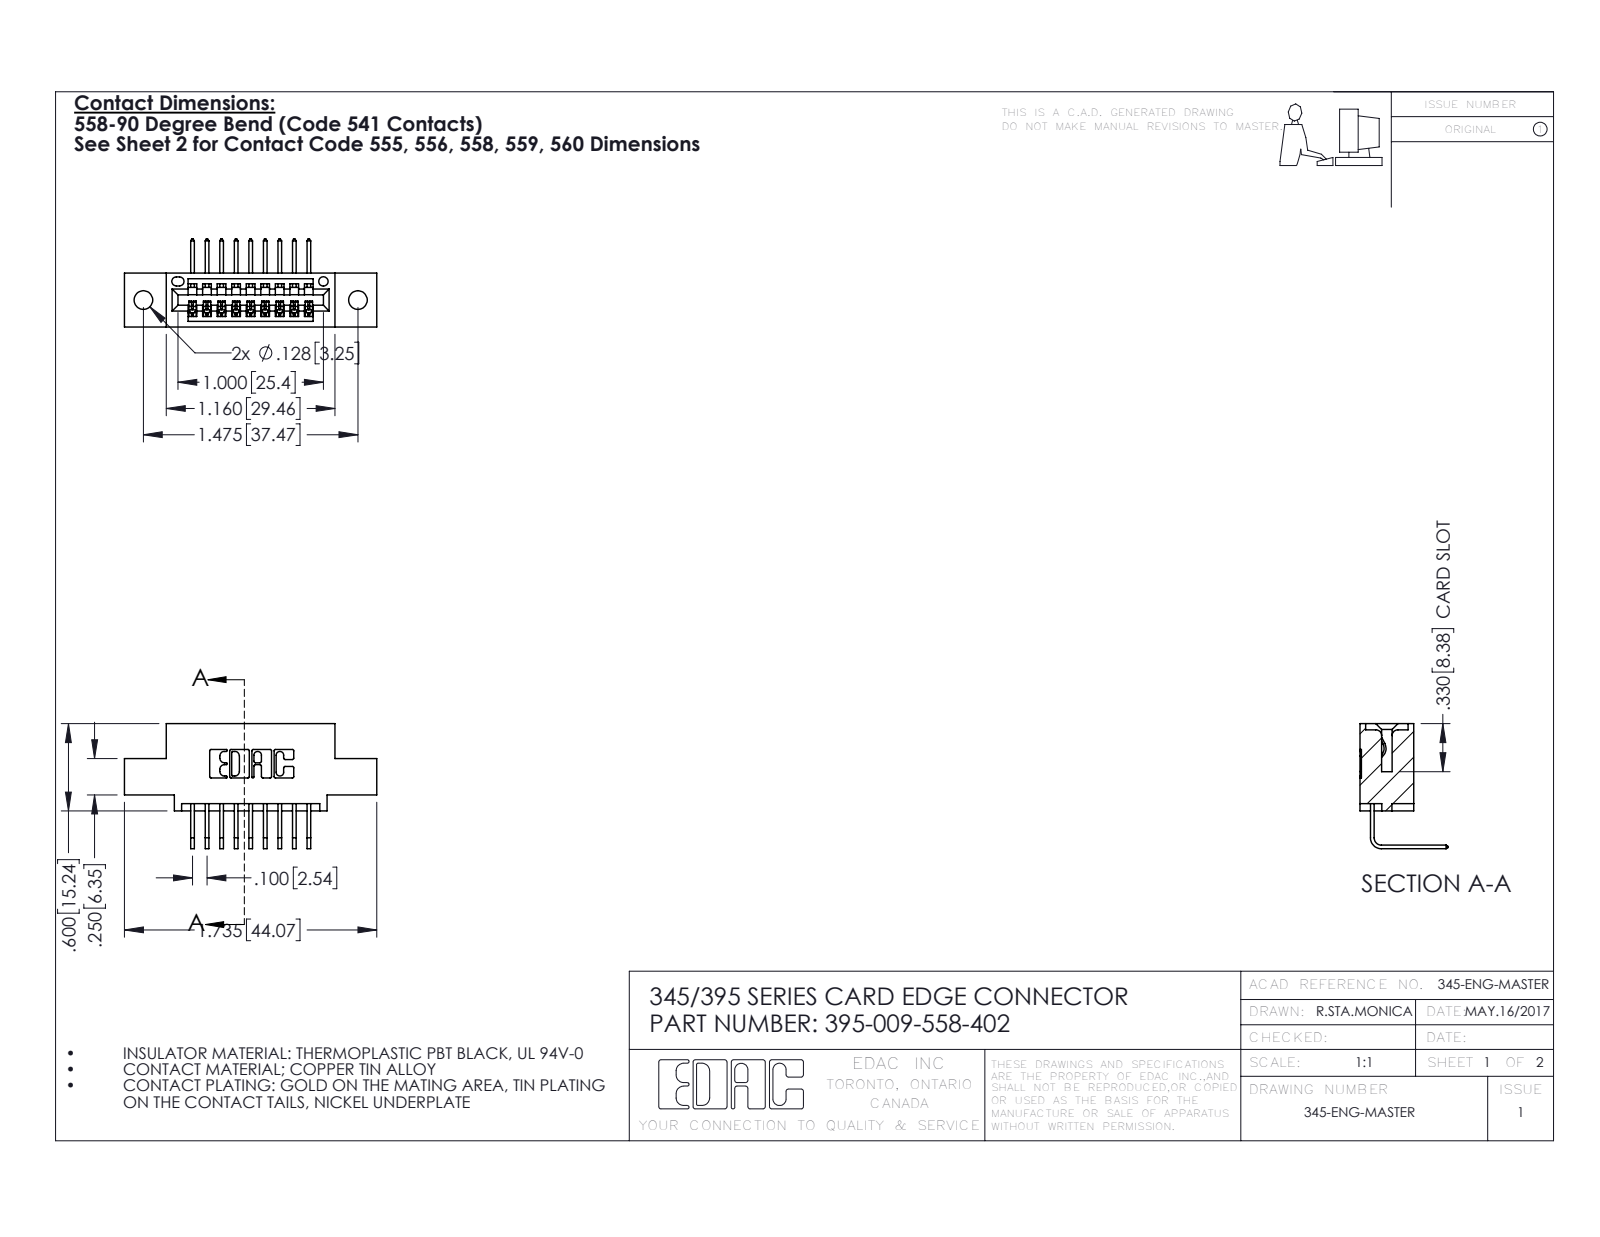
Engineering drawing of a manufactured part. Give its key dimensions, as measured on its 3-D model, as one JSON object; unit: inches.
{"part_name": "395-009-558-402; 345-292-001_558 Tail - 2; 345 Part_0.110 Offset - 0.128 Dia", "step_written_by": "SolidWorks 2016 (CONFIG_CONTROL_DESIGN)", "units": "inches", "bodies": {"solids": 10, "faces": 670, "planar": 462, "cylindrical": 208, "other": 0}, "overall_size": [1.735, 0.859, 0.605], "volume_in3": 0.234, "surface_area_in2": 7.184, "round_holes": [[0.128, 2], [0.064, 1]], "partial_cylinders_radius": [[0.01, 22], [0.006, 18], [0.007, 6], [0.031, 6], [0.026, 3], [0.031, 2], [0.04, 2], [0.014, 1]], "face_to_face_distances": [0.2, 0.072, 0.298, 0.37, 0.1, 0.098, 0.272, 0.025, 0.6, 0.06], "hole_center_spacings": [0.27, 1.244, 1.475]}
